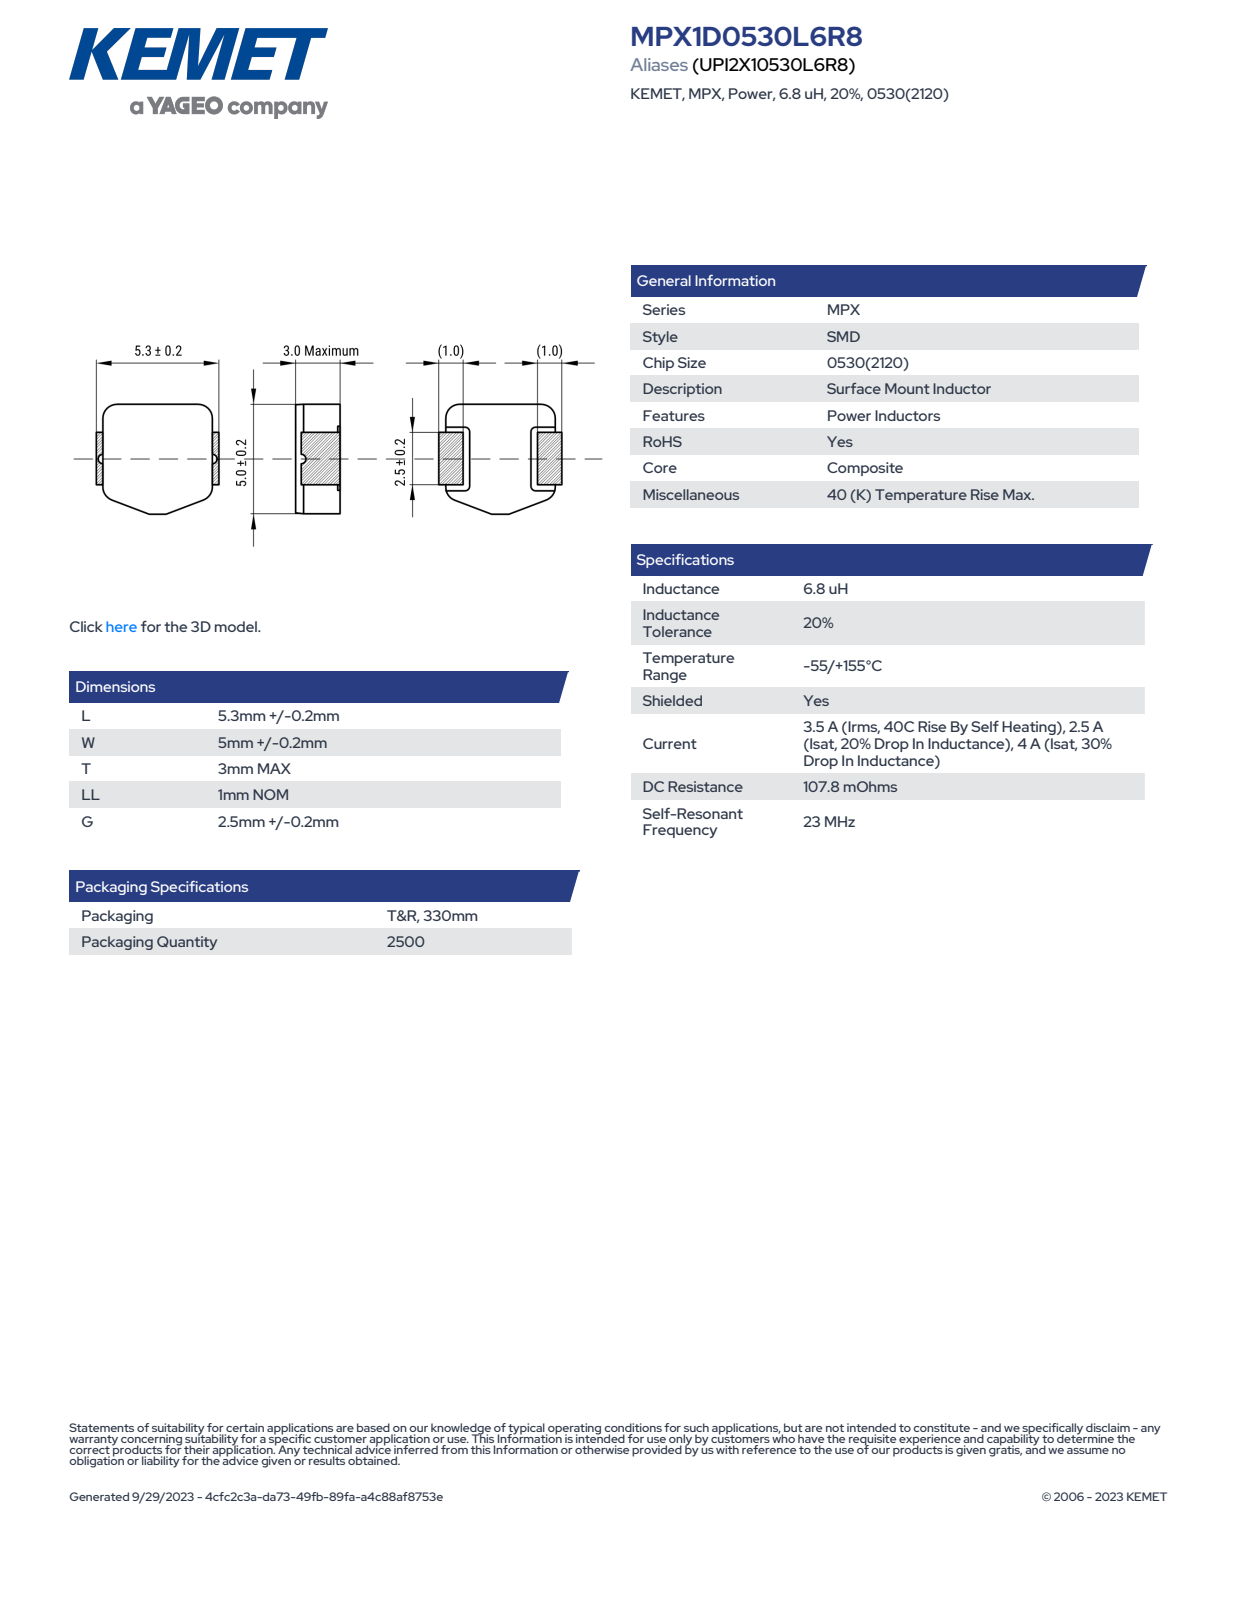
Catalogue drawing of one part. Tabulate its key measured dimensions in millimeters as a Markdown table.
| quantity | value |
| --- | --- |
| part name | MPX1D0530(KEMET) |
| STEP written by | SolidWorks 2018 (AUTOMOTIVE_DESIGN) |
| units | millimeters |
| bodies | 1 solid, 124 faces (100 planar, 24 cylindrical, 0 other) |
| overall size | 5.5 × 5.2 × 3 |
| volume | 73 mm³ |
| surface area | 106 mm² |
| partial cylindrical surfaces (radius × count) | 0.71 × 6, 0.75 × 6, 0.11 × 4, 0.2 × 4, 0.23 × 1 |
| main face-to-face distances | 2.96, 3, 5.5, 2.89, 1.72, 2.7, 1, 4.5, 1.68, 1.61 |
